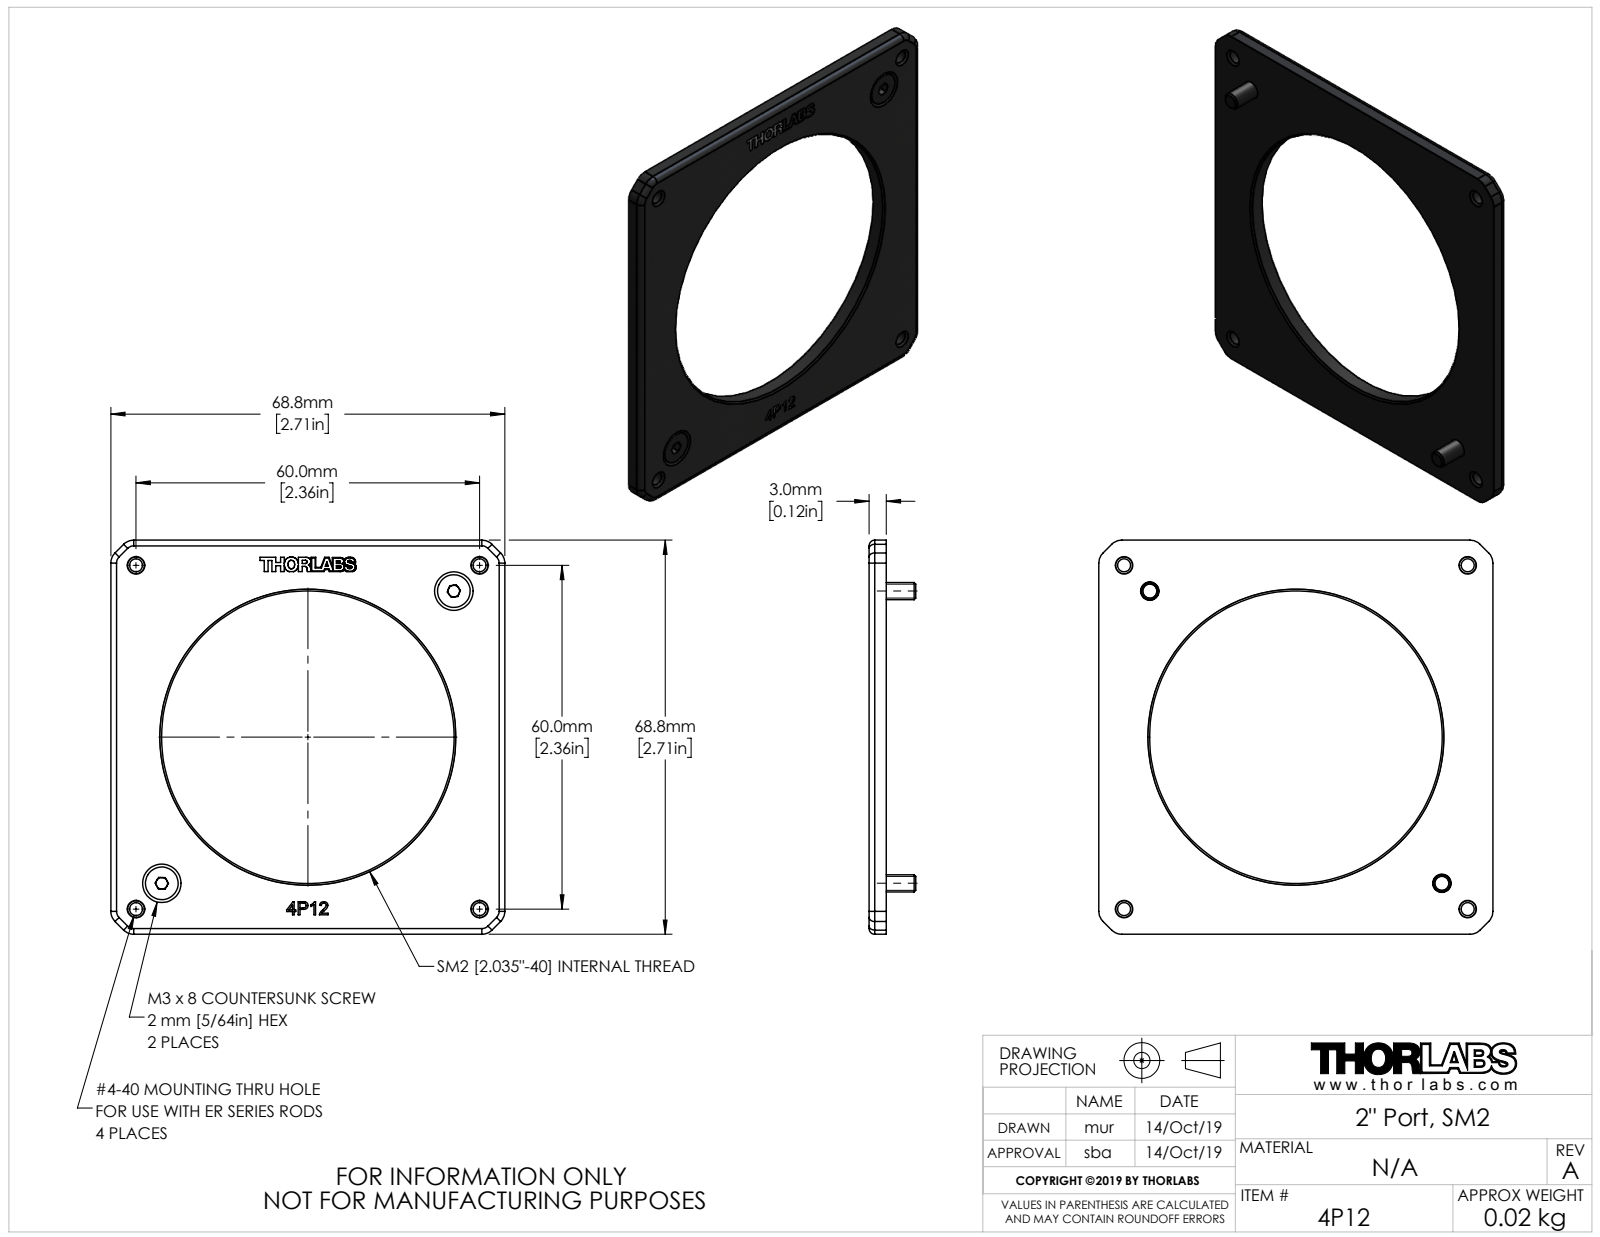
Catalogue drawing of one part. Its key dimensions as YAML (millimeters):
part_name: "19.11.04_4P12_2 Inch Aperture Port WEB"
step_written_by: "SolidWorks 2018 (AUTOMOTIVE_DESIGN)"
units: millimeters
bodies: {solids: 3, faces: 650, planar: 547, cylindrical: 38, other: 65}
overall_size: [68.8, 68.8, 8.16]
volume: 7918
surface_area: 6764
round_holes:
  - {diameter: 2.26, count: 4}
  - {diameter: 3.2, count: 2}
  - {diameter: 51.08, count: 1}
round_bosses_or_shafts:
  - {diameter: 5.7, count: 2}
  - {diameter: 3, count: 2}
partial_cylinders:
  - {radius: 1, count: 8}
  - {radius: 2.5, count: 8}
face_to_face_distances: [3, 68.8, 2.84, 2.99, 5.16, 8.16, 8.15, 8, 93.08, 2.02]
hole_center_spacings: [42.43, 55.68, 60, 6.36, 36.06, 78.49, 84.85, 72.12]
